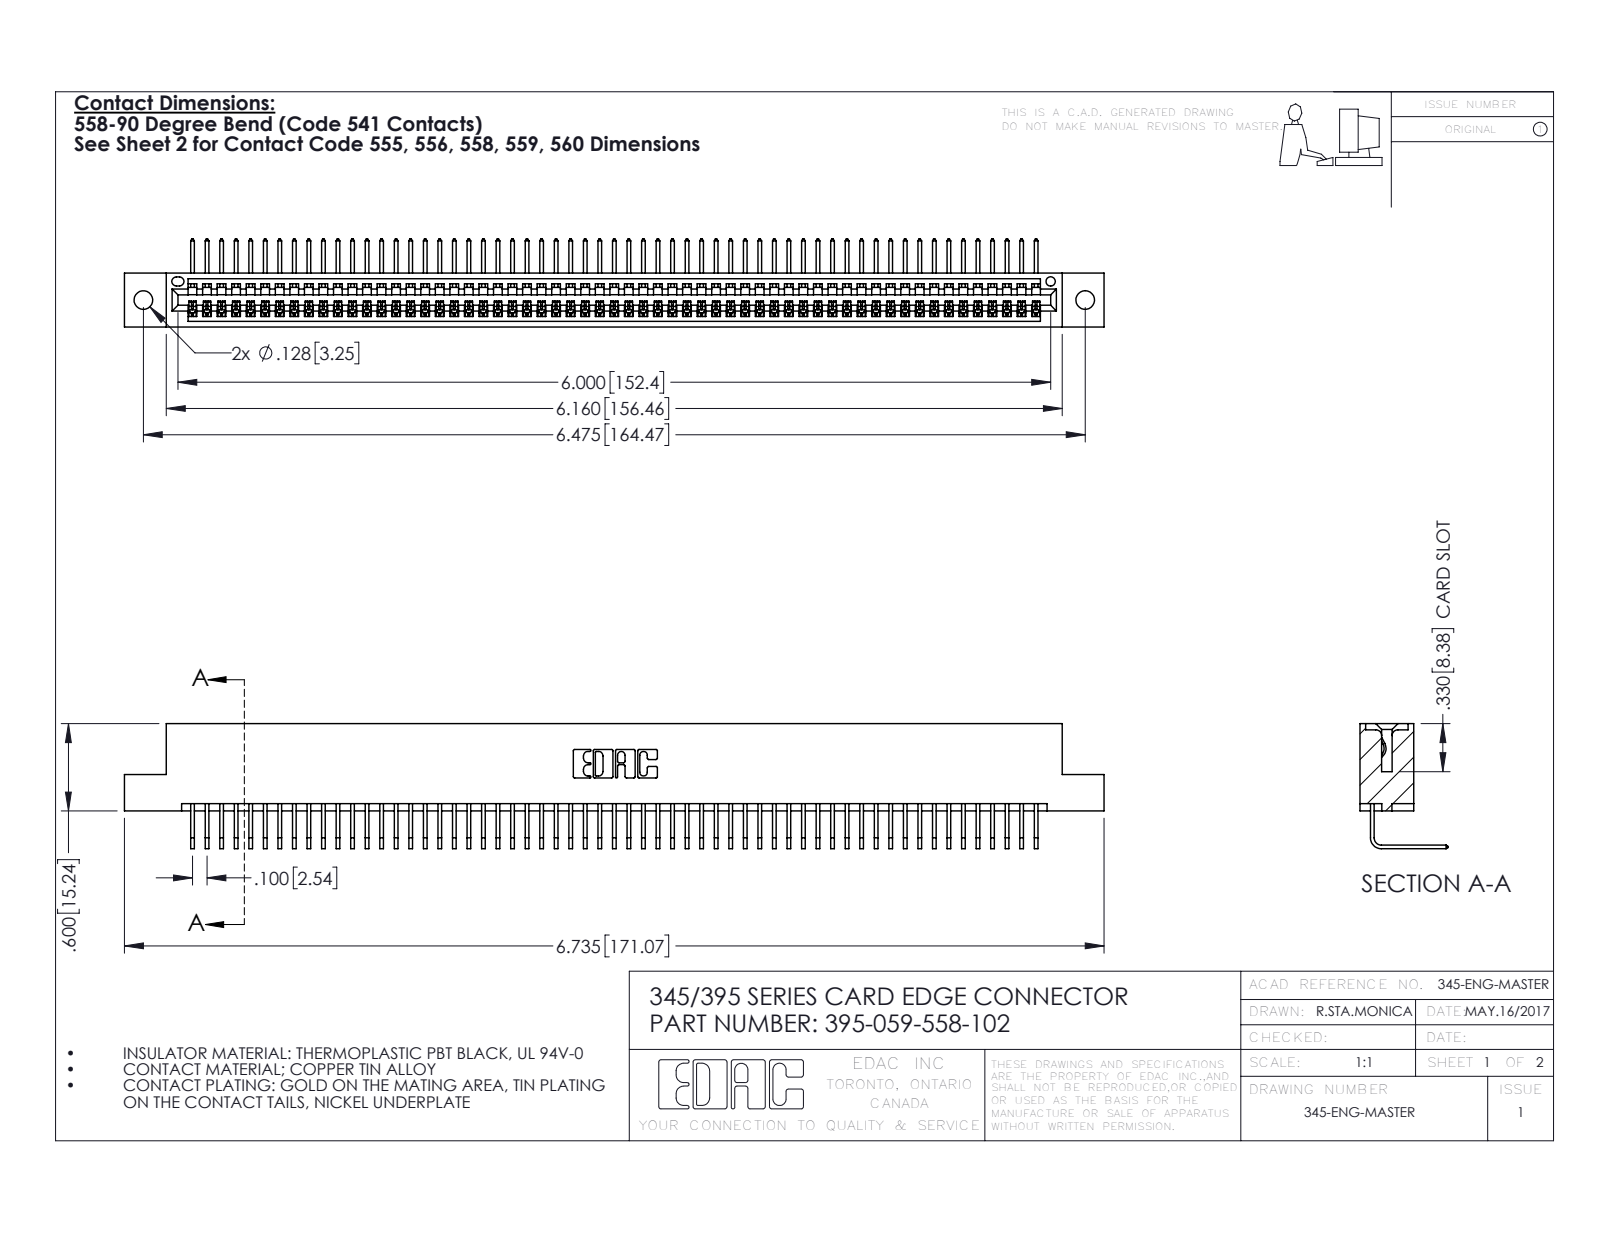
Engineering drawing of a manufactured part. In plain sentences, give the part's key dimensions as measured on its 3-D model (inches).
The part is named "345-292-001_558 Tail - 2; 395-059-558-102; 345 Part_Flush Mounting Lugs - 0.128 Dia". Its 3-D file was written by "SolidWorks 2016 (CONFIG_CONTROL_DESIGN)". It is 60 solids with 3666 faces: 2558 planar, 1108 cylindrical and 0 other. Overall it measures 6.735 by 0.859 by 0.605 inches. Its volume is 1.01 cubic inches and its surface area 35.81 square inches. Round holes: 2 of diameter 0.128, 1 of diameter 0.064. Partial cylindrical surfaces (rounded edges, fillets, slot ends): 118 of radius 0.006, 22 of radius 0.01, 6 of radius 0.007, 6 of radius 0.031, 3 of radius 0.026, 2 of radius 0.031, 2 of radius 0.04, 1 of radius 0.014. The main face-to-face distances are 0.298, 0.072, 0.37, 0.2, 0.098, 0.272, 0.025, 0.225, 0.149, 0.072. The hole center spacings are 0.27, 6.239, 6.475.
